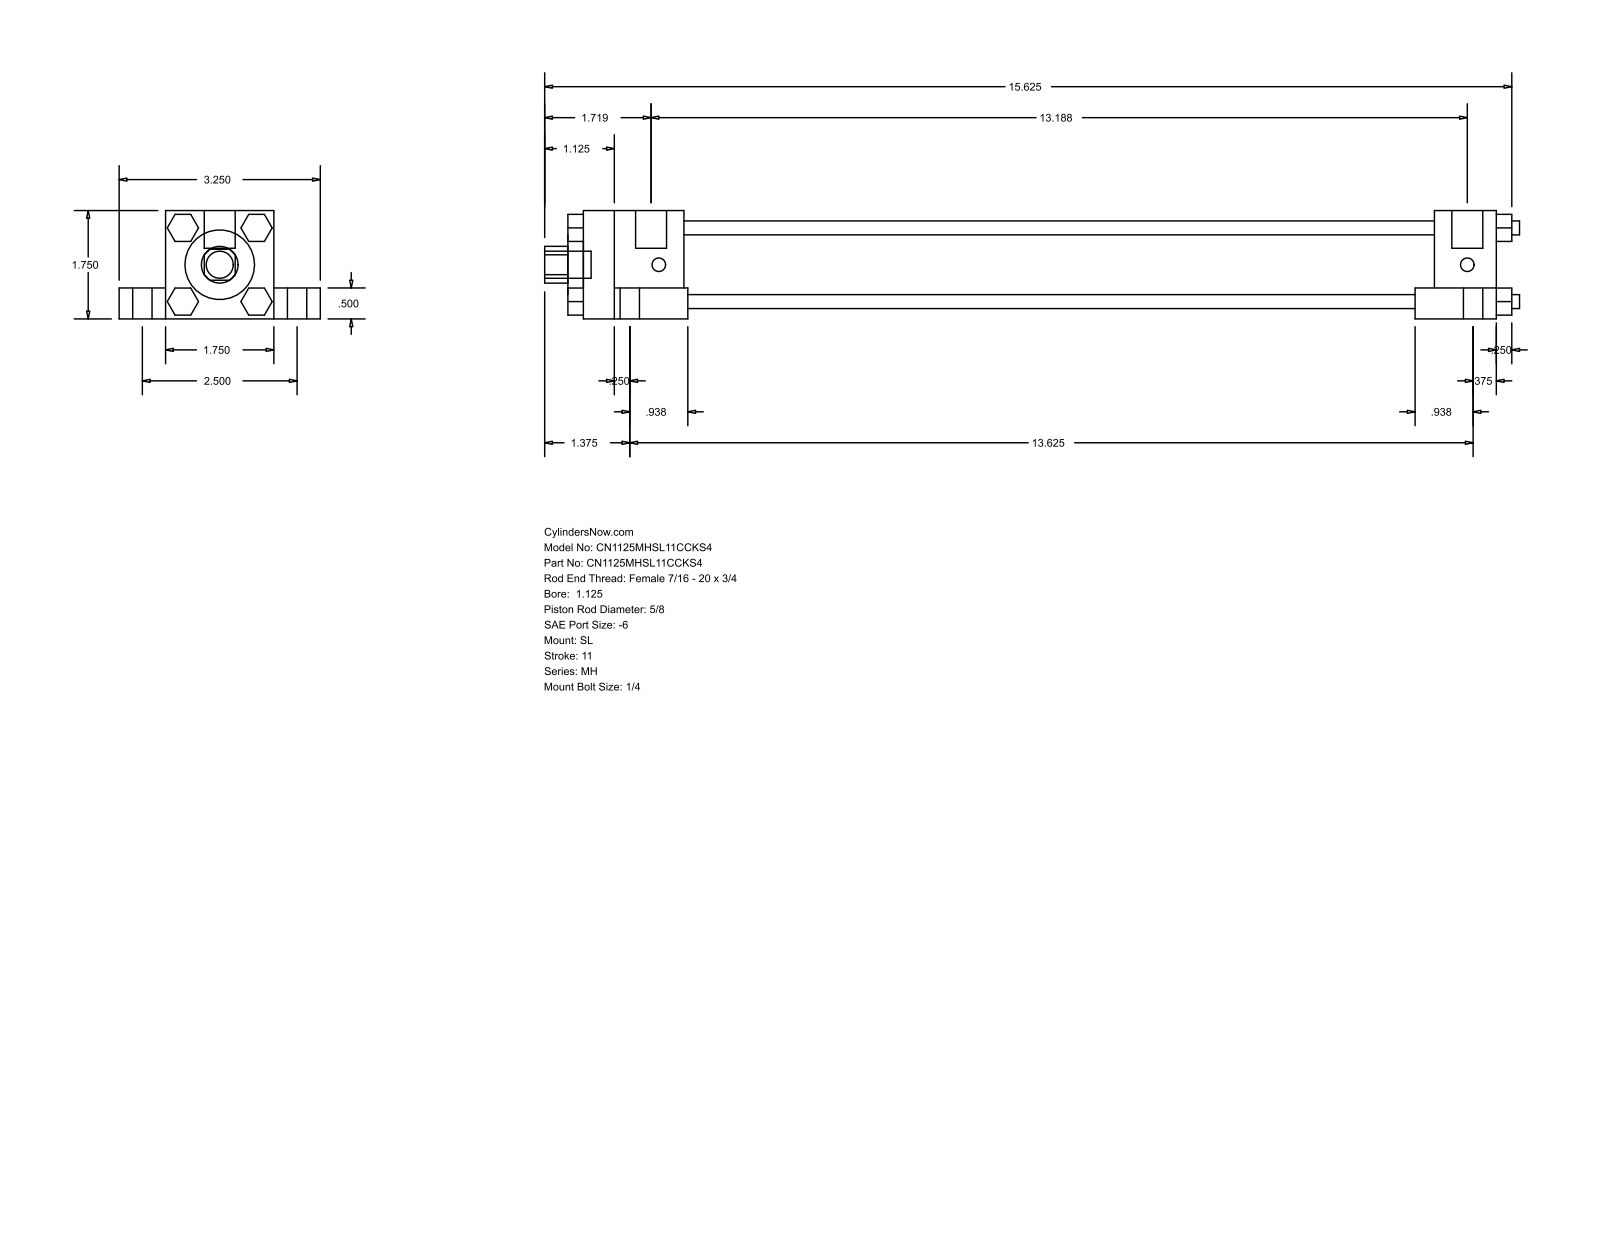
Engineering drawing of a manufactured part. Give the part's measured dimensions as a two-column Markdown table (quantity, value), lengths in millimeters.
| quantity | value |
| --- | --- |
| part name | MH_SL__0112_0.625 |
| STEP written by | GSSL Pune (CONFIG_CONTROL_DESIGN) |
| units | millimeters |
| bodies | 0 solids, 150 faces (114 planar, 36 cylindrical, 0 other) |
| overall size | 400.05 × 82.55 × 44.45 |
| round holes (diameter × count) | 15.88 × 1, 28.57 × 1, 34.92 × 1 |
| round bosses / shafts (diameter × count) | 14.29 × 4, 7.94 × 4, 5.71 × 4, 5.56 × 4, 12.7 × 2, 11.11 × 1 |
| partial cylindrical surfaces (radius × count) | 7.54 × 1 |
| main face-to-face distances | 44.46, 31.76, 19.04, 12.7, 63.5, 11.11, 307.97, 333.37, 25.4, 41.27 |
